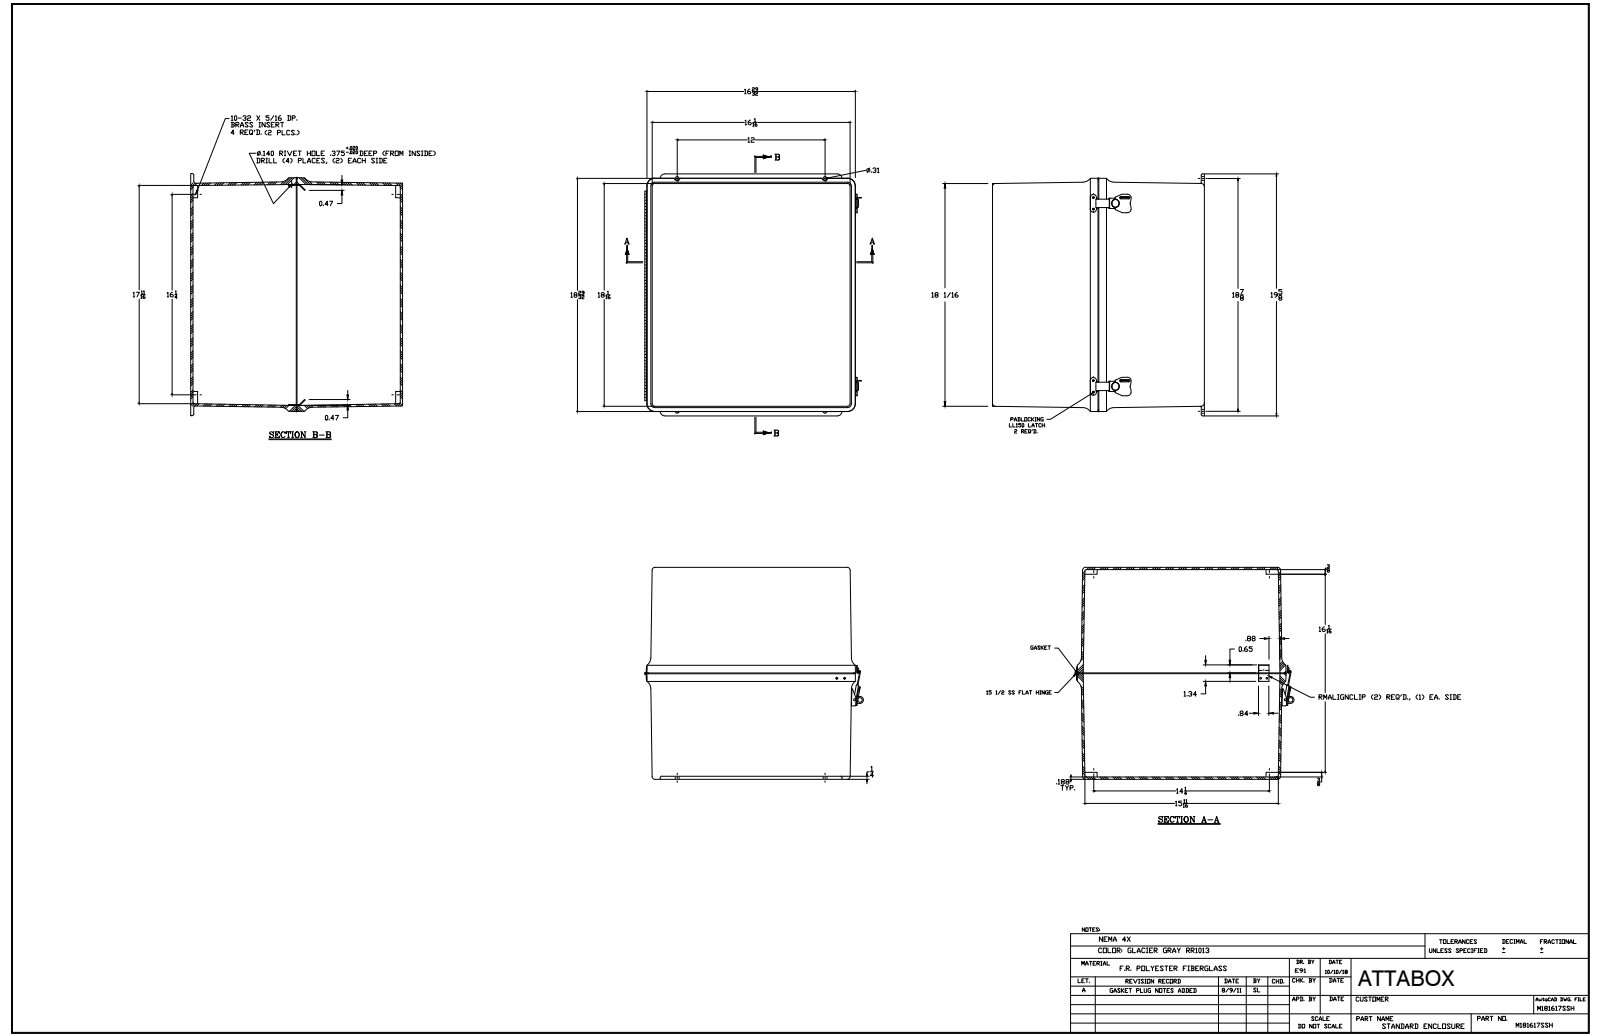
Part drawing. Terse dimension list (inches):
name: M181617SSH
written by: SolidWorks 2018 (AUTOMOTIVE_DESIGN)
unit: in
bodies: 62 solids, 1735 faces (706 planar, 673 cylindrical, 356 other)
size: 19.625 × 17.675 × 17.185
volume: 362.9 in³; area: 3 682 in²
holes: 26× ⌀0.14, 12× ⌀0.136, 12× ⌀0.152, 7× ⌀0.156, 4× ⌀0.13, 4× ⌀0.165, 4× ⌀0.197, 4× ⌀0.218, 2× ⌀0.118, 2× ⌀0.138, 2× ⌀0.193, 2× ⌀0.531
bosses: 24× ⌀0.25, 16× ⌀0.125, 8× ⌀0.125, 7× ⌀0.27, 2× ⌀0.583, 2× ⌀0.524, 2× ⌀0.209, 2× ⌀0.185
rounds: 88× R0.031, 19× R0.079, 16× R0.25, 14× R0.75, 12× R0.125, 8× R0.037, 8× R0.039, 8× R0.045
face distances: 0.187, 16.126, 18.126, 15.939, 17.185, 0.188, 16.997, 16.809, 16.997, 17.939
hole spacings: 9.75, 14.984, 1.37, 3.375, 3.375, 6.75, 21.613, 15.249
